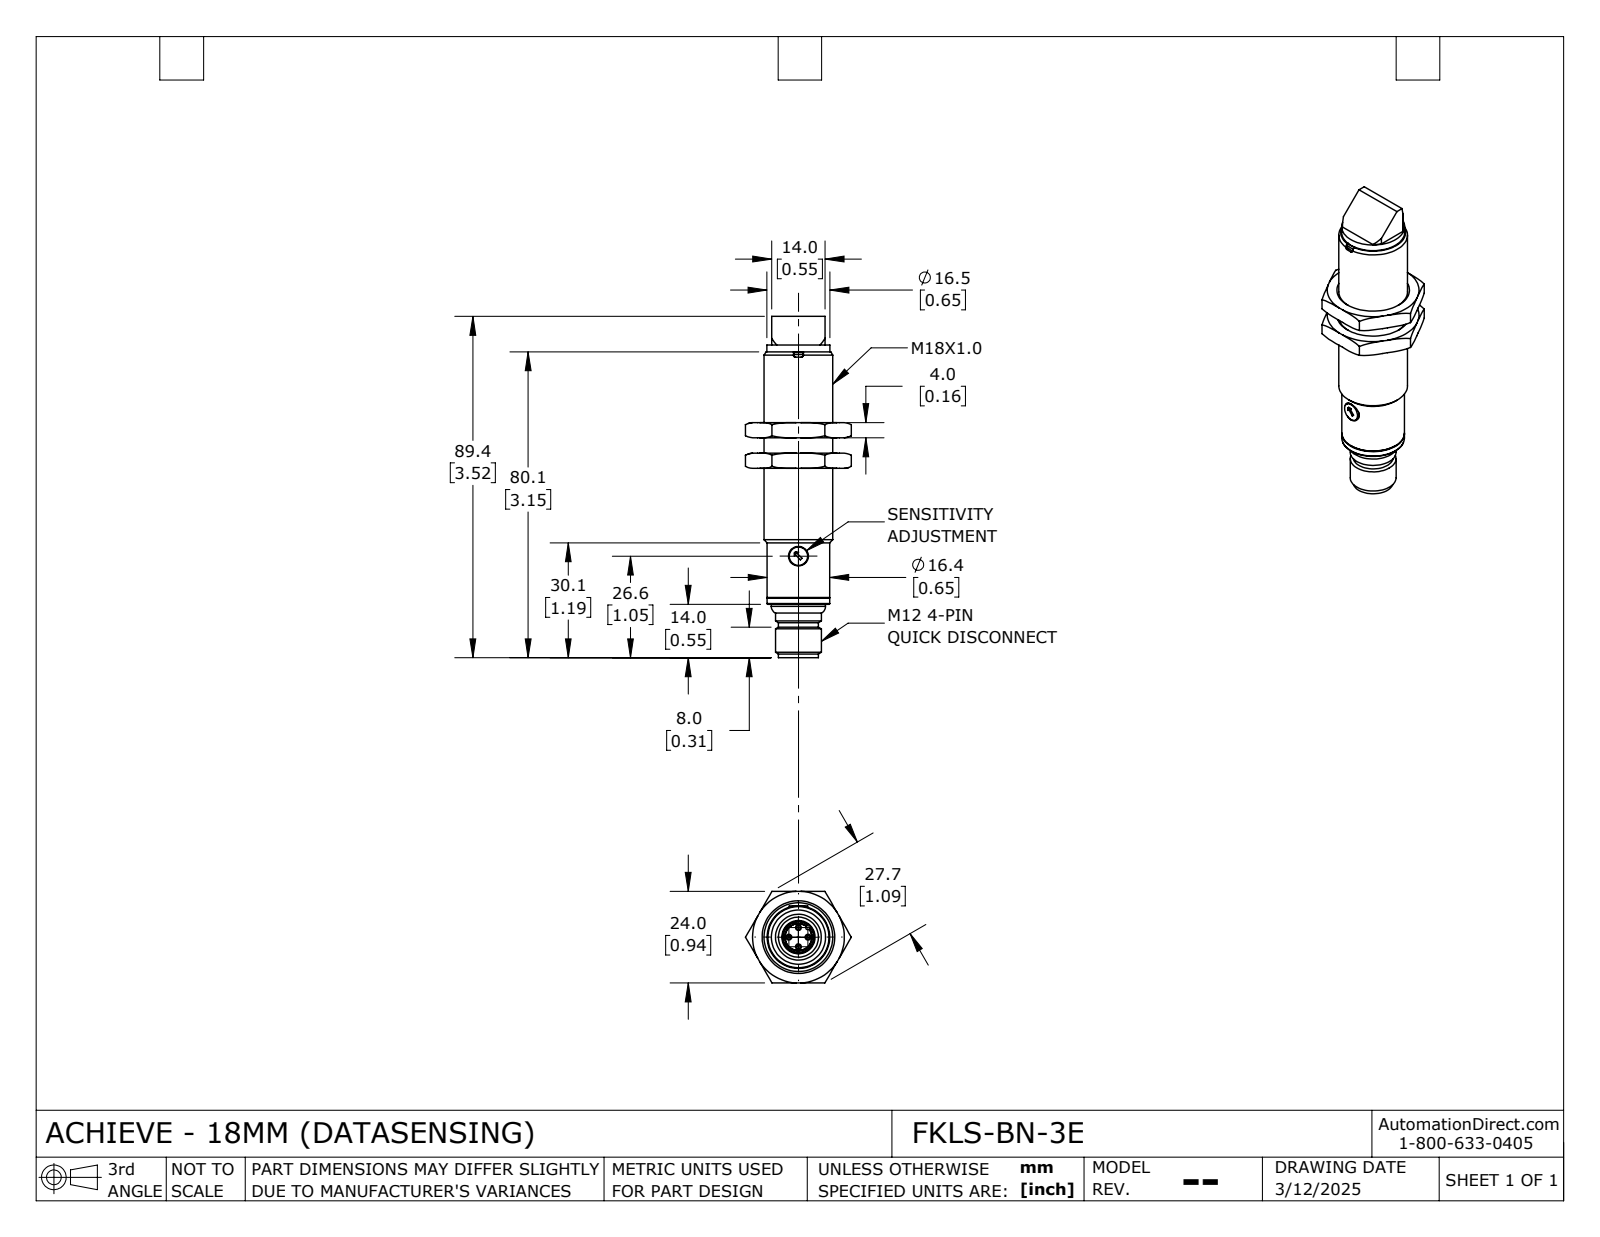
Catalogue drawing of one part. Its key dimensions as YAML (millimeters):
part_name: "FKLS-BN-3E_Default"
step_written_by: "SolidWorks 2024 (CONFIG_CONTROL_DESIGN)"
units: millimeters
bodies: {solids: 4, faces: 155, planar: 67, cylindrical: 35, other: 53}
overall_size: [89.4, 27.7, 24]
volume: 20170
surface_area: 8800
round_holes:
  - {diameter: 2.7, count: 1}
  - {diameter: 4.7, count: 1}
  - {diameter: 7.1, count: 1}
  - {diameter: 8.3, count: 1}
  - {diameter: 15, count: 1}
  - {diameter: 15.8, count: 1}
  - {diameter: 18, count: 1}
round_bosses_or_shafts:
  - {diameter: 1, count: 4}
  - {diameter: 16.5, count: 1}
  - {diameter: 16.4, count: 1}
  - {diameter: 14.2, count: 1}
  - {diameter: 12, count: 1}
  - {diameter: 10.5, count: 1}
  - {diameter: 7, count: 1}
  - {diameter: 4.8, count: 1}
partial_cylinders:
  - {radius: 0.5, count: 4}
  - {radius: 0.6, count: 1}
  - {radius: 8.1, count: 1}
  - {radius: 8.4, count: 1}
face_to_face_distances: [4, 8, 24, 12, 2.9, 0.4, 3.3, 2.8, 2.4, 0.5]
